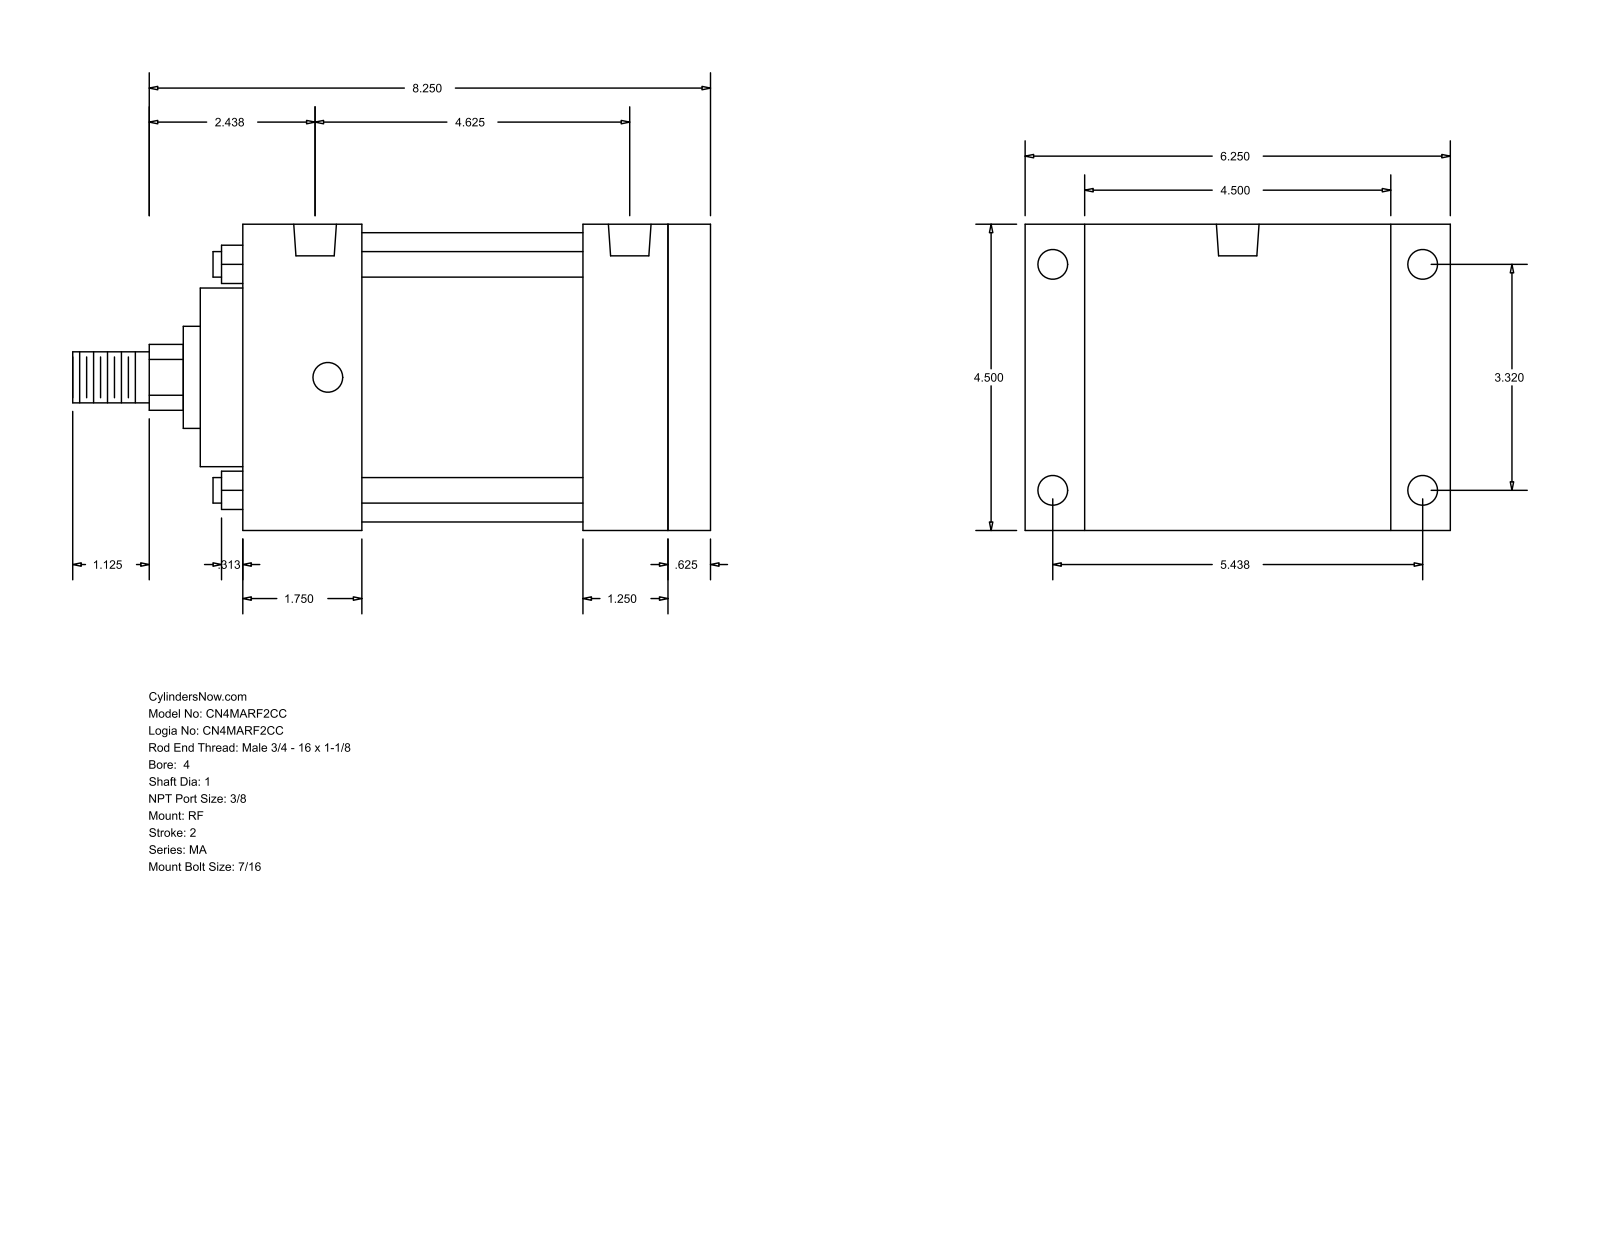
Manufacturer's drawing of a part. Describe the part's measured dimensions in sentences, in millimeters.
The part is named "MA_RF__0400_1". Its 3-D file was written by "GSSL Pune (CONFIG_CONTROL_DESIGN)". It is 0 solids with 94 faces: 65 planar, 29 cylindrical and 0 other. Overall it measures 238.12 by 158.75 by 114.3 millimeters. Round holes: 8 of diameter 11.11, 2 of diameter 15.93. Round bosses or shafts: 4 of diameter 9.53, 1 of diameter 107.95, 1 of diameter 66.67, 1 of diameter 38.1, 1 of diameter 25.4, 1 of diameter 19.05. Partial cylindrical surfaces (rounded edges, fillets, slot ends): 1 of radius 12.29. The main face-to-face distances are 114.3, 174.63, 15.87, 158.76, 47.62, 22.23, 136.53, 127.01, 31.75, 44.46. The hole center spacings are 84.32, 107.95, 138.12, 161.82, 4.76, 4.77, 112.71, 112.72.
